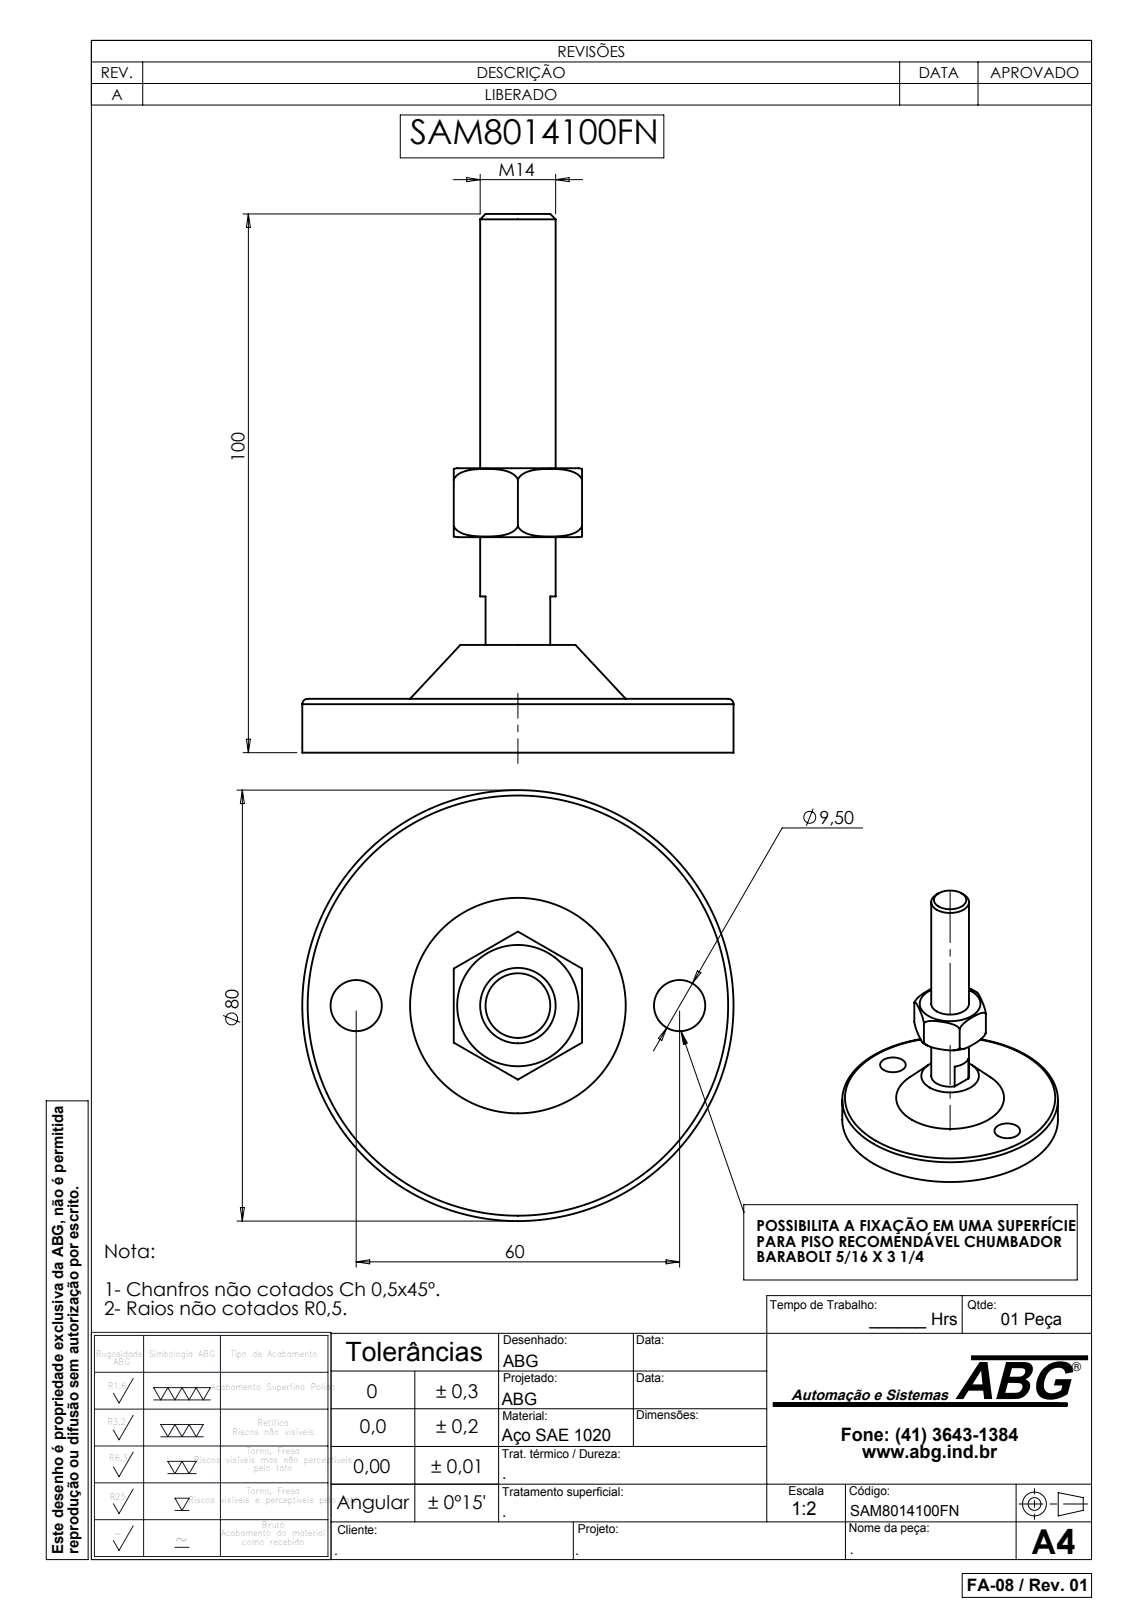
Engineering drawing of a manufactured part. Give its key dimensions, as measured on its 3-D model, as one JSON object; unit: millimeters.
{"part_name": "SAM8014100FN", "step_written_by": "SolidWorks 2007 (CONFIG_CONTROL_DESIGN)", "units": "millimeters", "bodies": {"solids": 1, "faces": 36, "planar": 16, "cylindrical": 10, "other": 10}, "overall_size": [100, 76, 76], "volume_mm3": 67985, "surface_area_mm2": 16694, "round_holes": [[9.5, 2]], "round_bosses_or_shafts": [[76, 1], [14, 1]], "face_to_face_distances": [10, 23.8, 20, 52.8, 42.8, 40, 30, 12.8, 32.8, 5.9], "hole_center_spacings": [56.56]}
